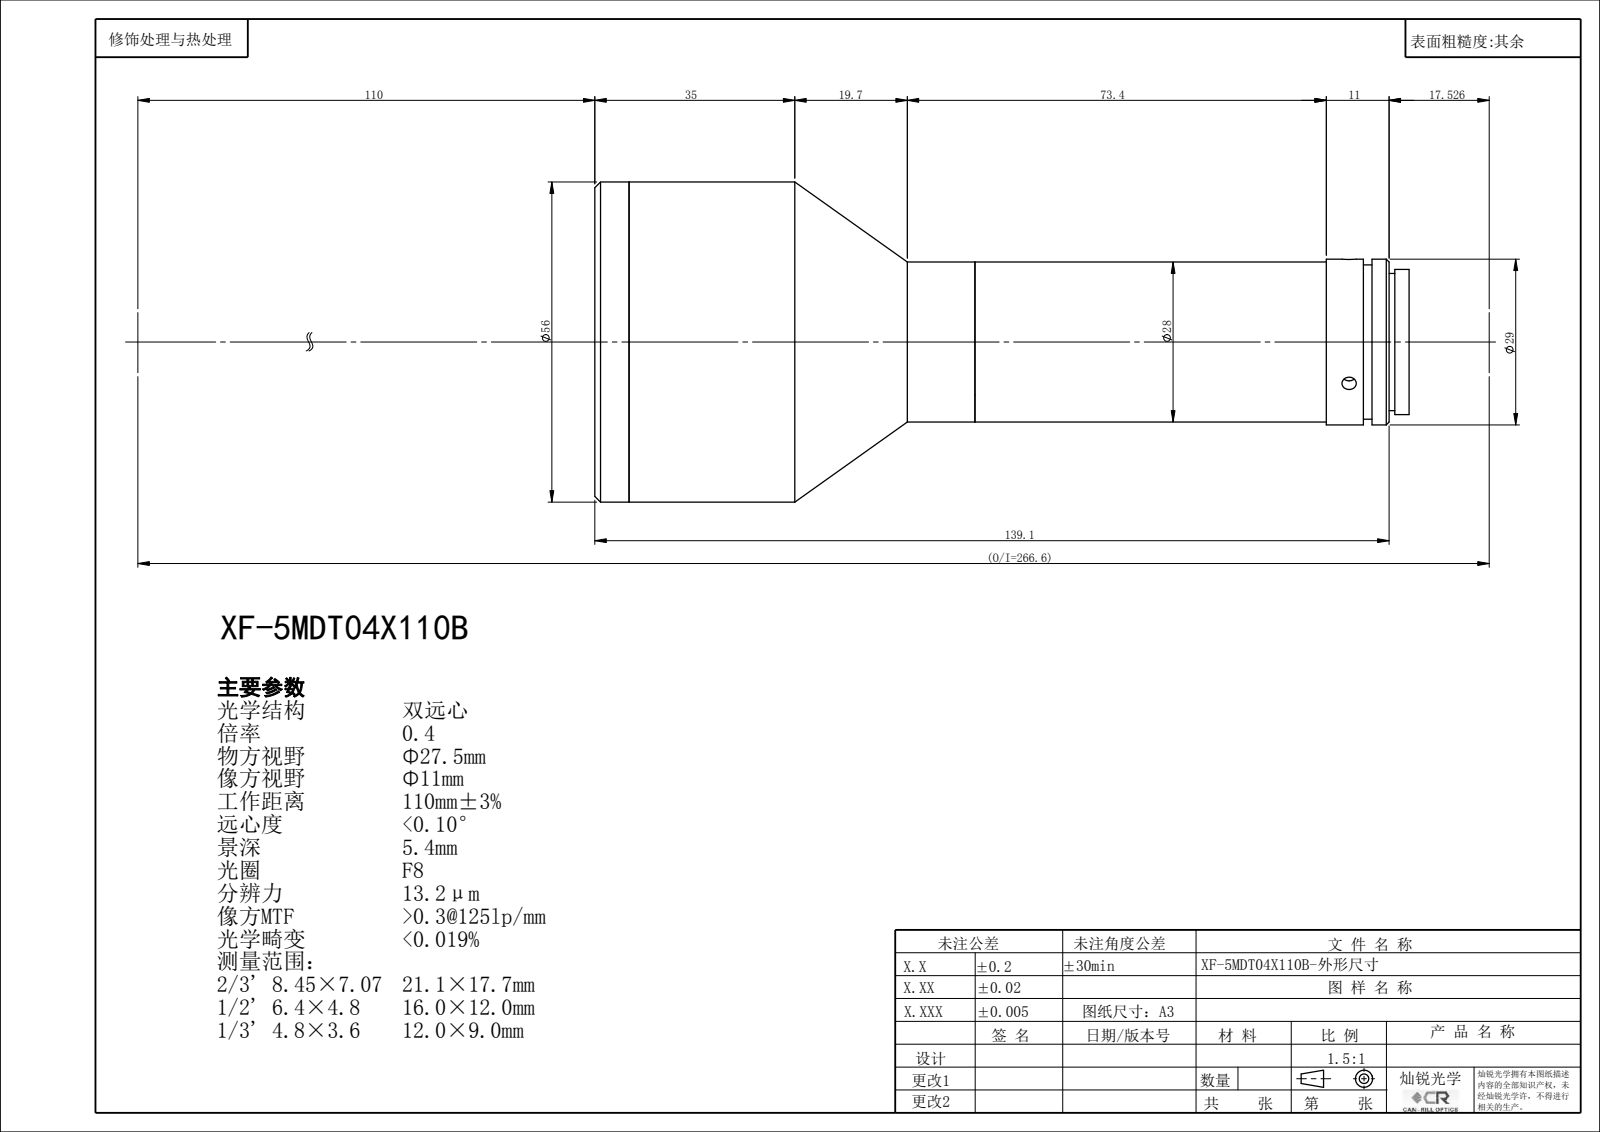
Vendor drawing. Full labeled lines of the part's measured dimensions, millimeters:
STEP written by: SolidWorks 2014 (CONFIG_CONTROL_DESIGN)
Units: millimetres
Bodies: 0 solids, 76 faces (28 planar, 40 cylindrical, 8 other)
Overall size (bounding box): 142.55 × 56 × 56
Round holes (diameter × count): ⌀2.5 ×3, ⌀15.5 ×1, ⌀17.4 ×1, ⌀19 ×1, ⌀21.4 ×1, ⌀46 ×1, ⌀49.4 ×1, ⌀52 ×1
Round bosses / shafts (diameter × count): ⌀56 ×1, ⌀29 ×1, ⌀28 ×1, ⌀27 ×1, ⌀25.4 ×1, ⌀24 ×1
Main face-to-face distances: 60.54, 6, 66.54, 2.38, 3.62, 64.16, 128.05, 125.67, 122.05, 61.51
